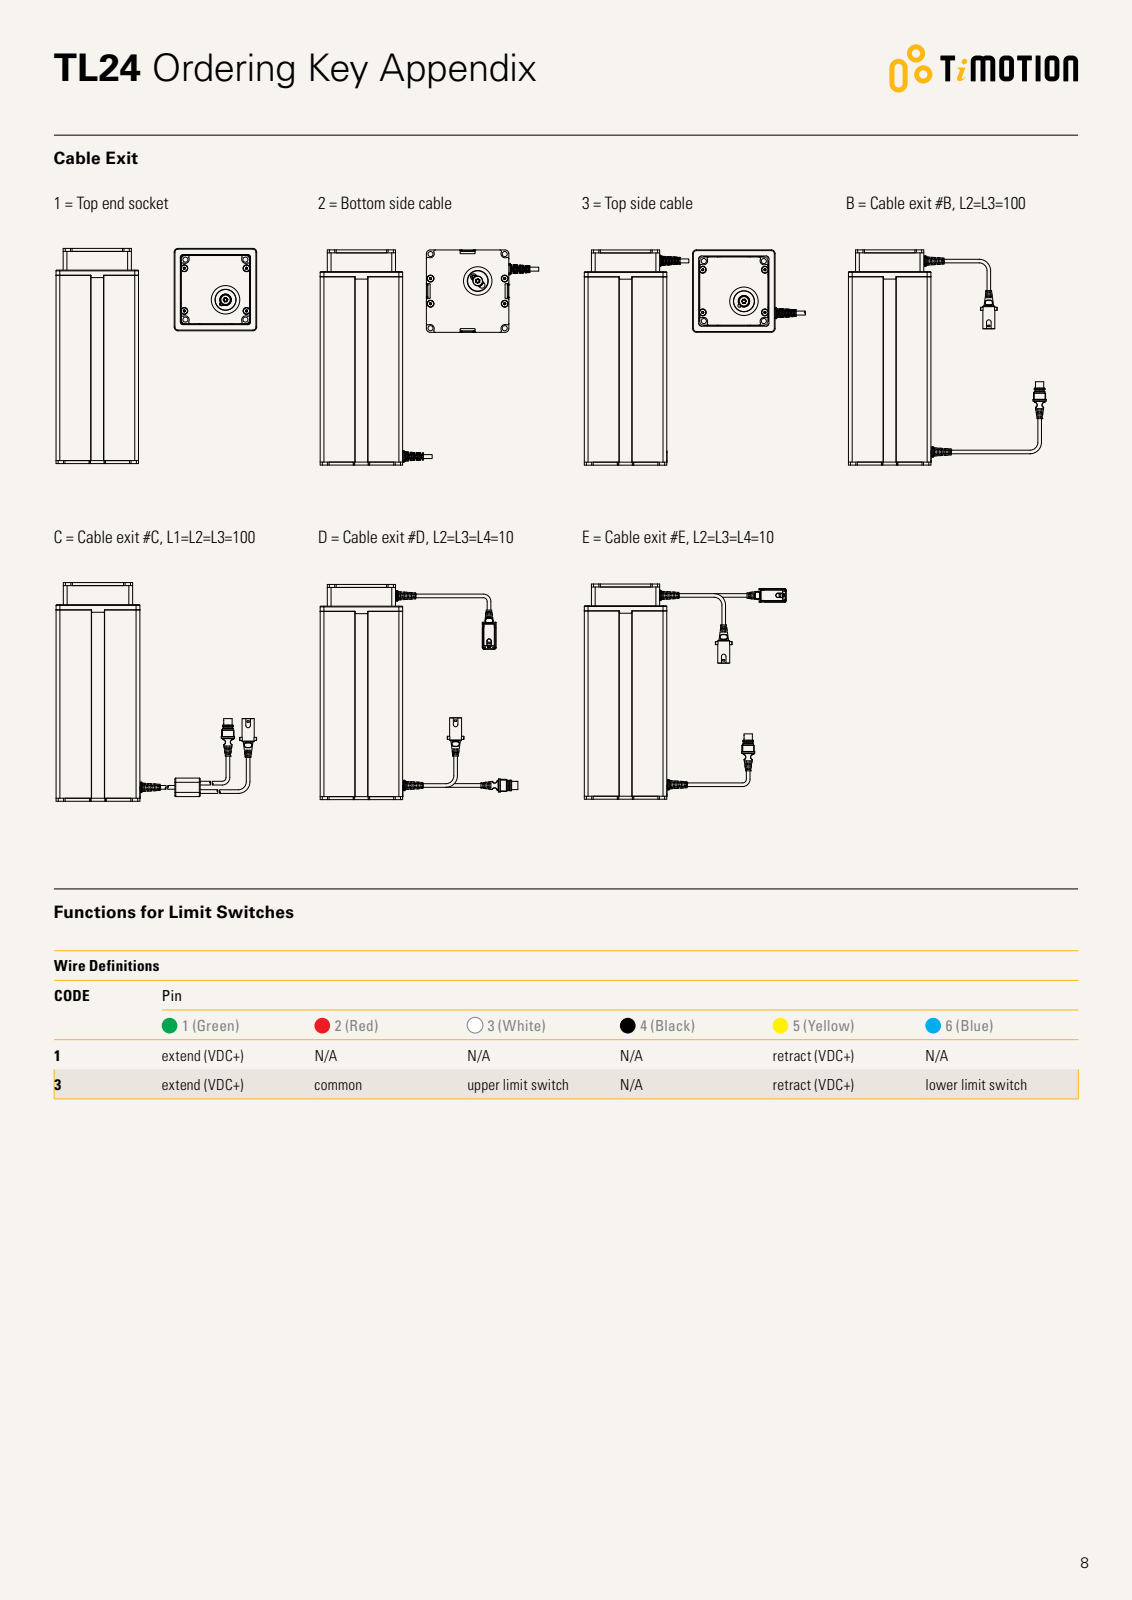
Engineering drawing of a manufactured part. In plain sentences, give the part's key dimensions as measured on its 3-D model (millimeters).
The part is named "33903-212-12; CBA三維零件圖-32906-307-底蓋-0; 33903-201; 三維零件圖-32906-306-上蓋-A (+7 more)". Its 3-D file was written by "SolidWorks 2015 (CONFIG_CONTROL_DESIGN)". It is 21 solids with 1899 faces: 695 planar, 884 cylindrical and 320 other. Overall it measures 300 by 151.39 by 151.39 millimeters. Its volume is 1 109 000 cubic millimeters and its surface area 575 457 square millimeters. Round holes: 8 of diameter 4.2, 8 of diameter 6.8, 8 of diameter 9.2, 4 of diameter 3.2, 4 of diameter 5.2, 4 of diameter 10, 3 of diameter 4, 1 of diameter 6.2, 1 of diameter 11, 1 of diameter 14, 1 of diameter 26. Round bosses or shafts: 12 of diameter 4, 4 of diameter 9.3, 2 of diameter 6, 1 of diameter 21.5, 1 of diameter 11.8, 1 of diameter 11, 1 of diameter 5.89, 1 of diameter 5.3. Partial cylindrical surfaces (rounded edges, fillets, slot ends): 256 of radius 0.2, 42 of radius 1, 40 of radius 2, 36 of radius 0.5, 20 of radius 0.3, 20 of radius 3, 17 of radius 5.5, 16 of radius 1.6. The main face-to-face distances are 100.51, 4, 9.5, 110.01, 86.51, 4.5, 3.5, 14, 2, 98.51. The hole center spacings are 90, 99, 19, 13.43, 14.17, 25.07, 32.7, 92.46.
